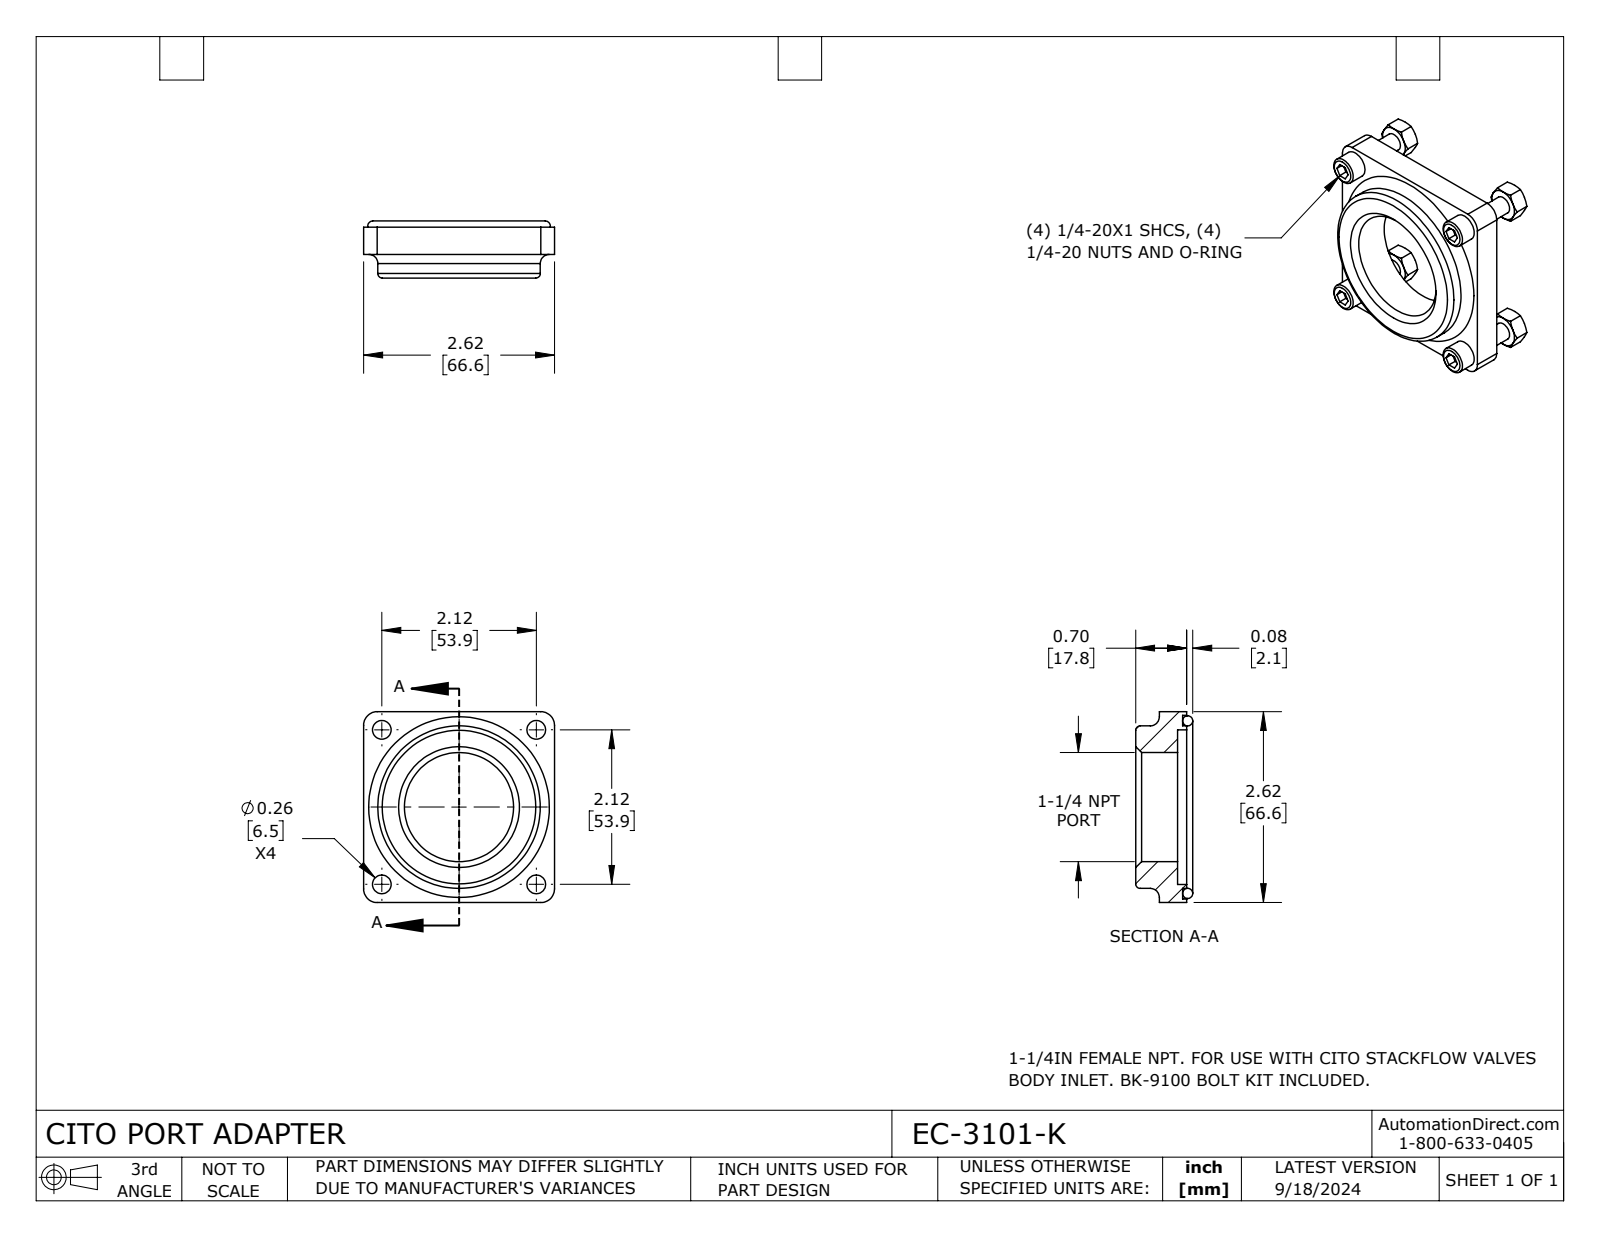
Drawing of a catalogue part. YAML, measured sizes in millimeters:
part_name: "EC-3101-K"
step_written_by: "SolidWorks 2023 (CONFIG_CONTROL_DESIGN)"
units: millimeters
bodies: {solids: 2, faces: 42, planar: 10, cylindrical: 22, other: 10}
overall_size: [66.6, 66.6, 19.9]
volume: 38720
surface_area: 15430
round_holes:
  - {diameter: 6.5, count: 4}
  - {diameter: 38.1, count: 1}
  - {diameter: 54, count: 1}
  - {diameter: 64.1, count: 1}
round_bosses_or_shafts:
  - {diameter: 56.7, count: 1}
partial_cylinders:
  - {radius: 4.7, count: 2}
  - {radius: 4.8, count: 2}
face_to_face_distances: [9.5, 6.4, 3.2, 66.6, 8.3, 14.6, 17.8, 16.4, 8.1, 1.8]
hole_center_spacings: [38.2, 53.9, 76.3]
